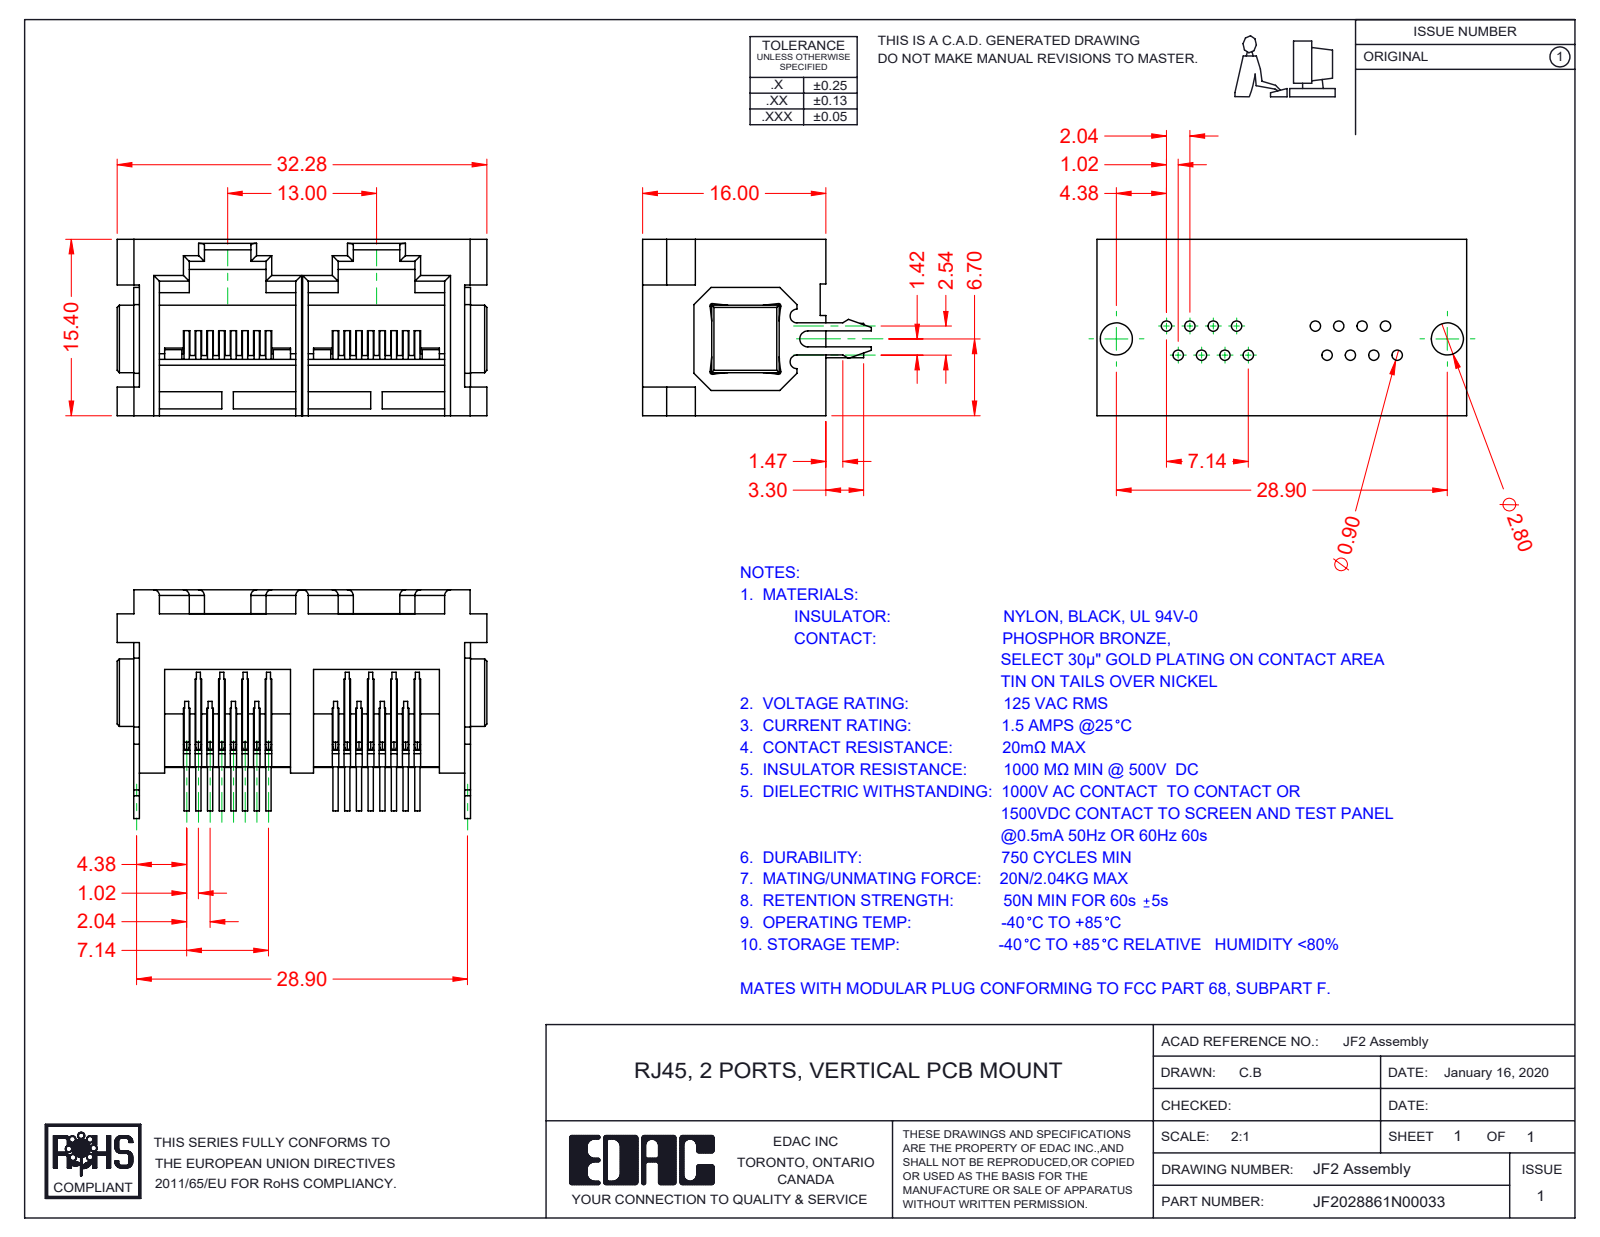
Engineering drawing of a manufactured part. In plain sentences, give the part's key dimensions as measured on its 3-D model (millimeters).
The part is named "F2 Contacts; RJF2028861N00033; F2 Contact Lock; F2 Insulator (+1 more)". Its 3-D file was written by "SolidWorks 2016 (CONFIG_CONTROL_DESIGN)". It is 21 solids with 1130 faces: 734 planar, 300 cylindrical and 96 other. Overall it measures 32.28 by 19.97 by 15.4 millimeters. Its volume is 3 519 cubic millimeters and its surface area 6 910 square millimeters. Round bosses or shafts: 64 of diameter 0.46. Partial cylindrical surfaces (rounded edges, fillets, slot ends): 32 of radius 0.18, 15 of radius 0.5, 4 of radius 0.2, 4 of radius 20.35, 3 of radius 0.3, 2 of radius 0.6, 1 of radius 0.21, 1 of radius 0.45. The main face-to-face distances are 12.59, 2.1, 13, 1.5, 2.81, 0.92, 11.67, 0.5, 28.4, 11.
